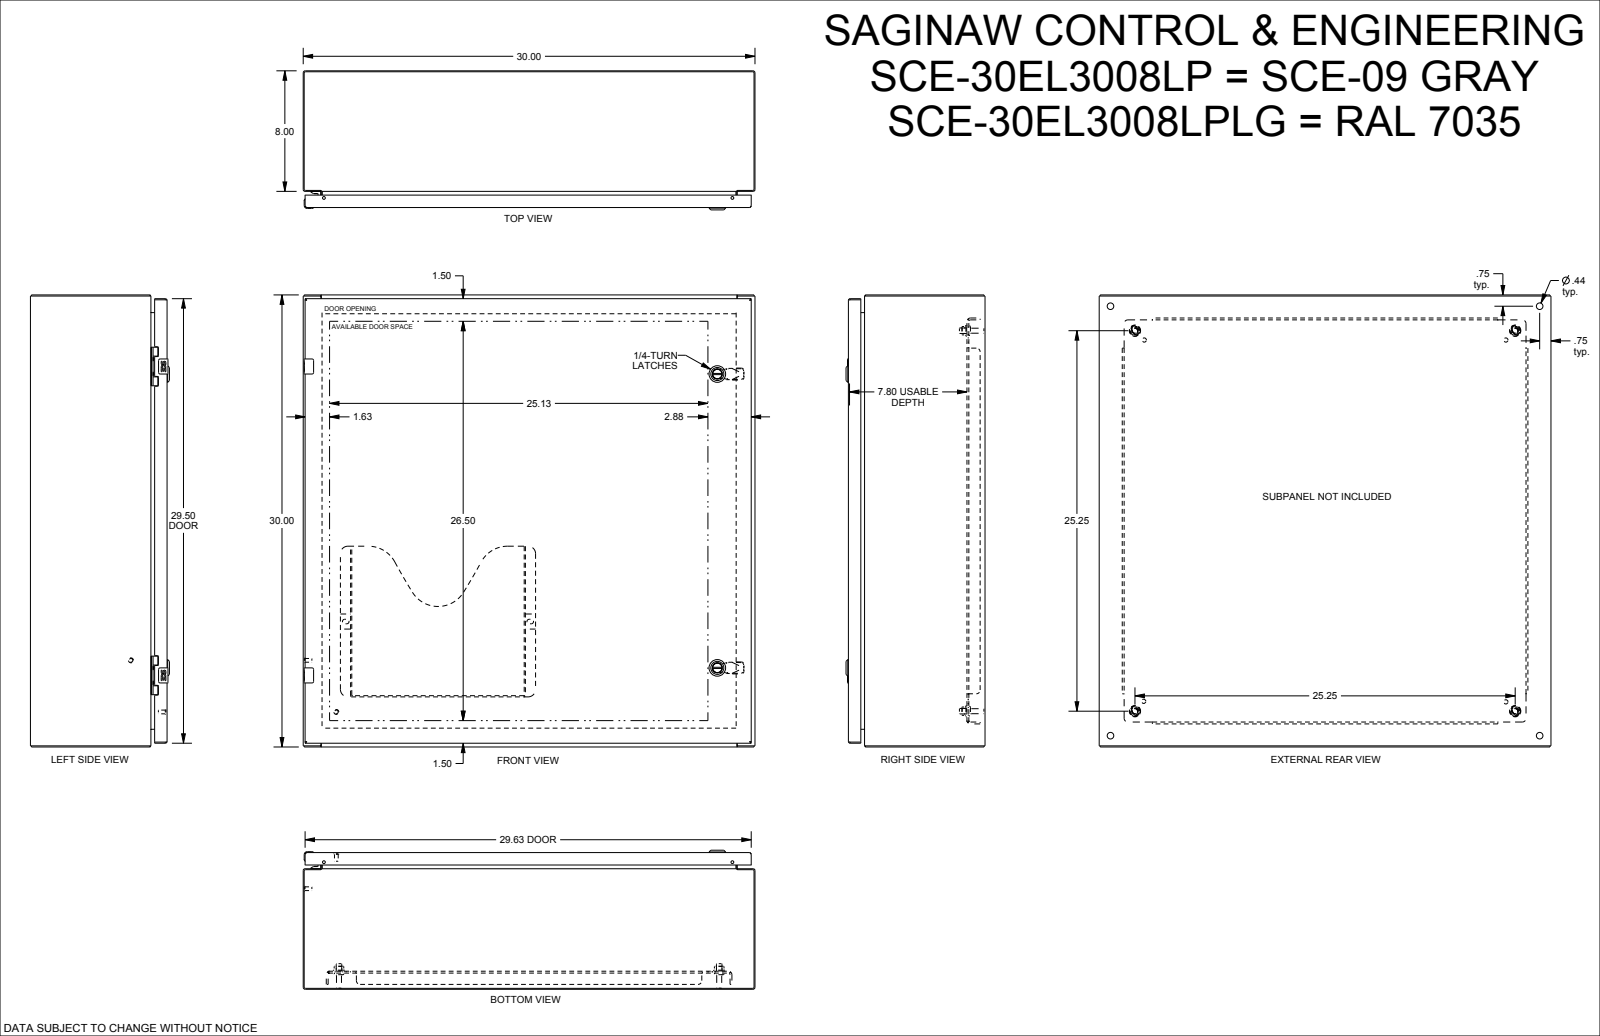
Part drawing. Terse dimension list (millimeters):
name: SCE-30EL3008LP
written by: SolidWorks 2021 (AUTOMOTIVE_DESIGN)
unit: mm
bodies: 47 solids, 2843 faces (1115 planar, 858 cylindrical, 870 other)
size: 762 × 762 × 234.4
volume: 5 734 000 mm³; area: 5 324 000 mm²
holes: 4× ⌀4.4, 4× ⌀5.2, 4× ⌀6.2, 4× ⌀6.8, 4× ⌀7.1, 4× ⌀9.3, 4× ⌀9.5, 4× ⌀11.1, 4× ⌀12.7, 2× ⌀1, 2× ⌀4.8, 2× ⌀5
bosses: 6× ⌀4.3, 4× ⌀9.3, 4× ⌀8.4, 4× ⌀6.4, 4× ⌀6.3, 4× ⌀6.1, 3× ⌀5, 2× ⌀28
rounds: 56× R0.3, 28× R0.3, 20× R0.4, 20× R0.5, 17× R1, 13× R1.5, 12× R0.7, 12× R2.5
face distances: 1.9, 1.5, 760.1, 230.5, 228.5, 228.9, 227, 30.5, 200, 25.4
hole spacings: 683.9, 25, 520.7, 625.8, 669.3, 0.5, 12.5, 12.5
